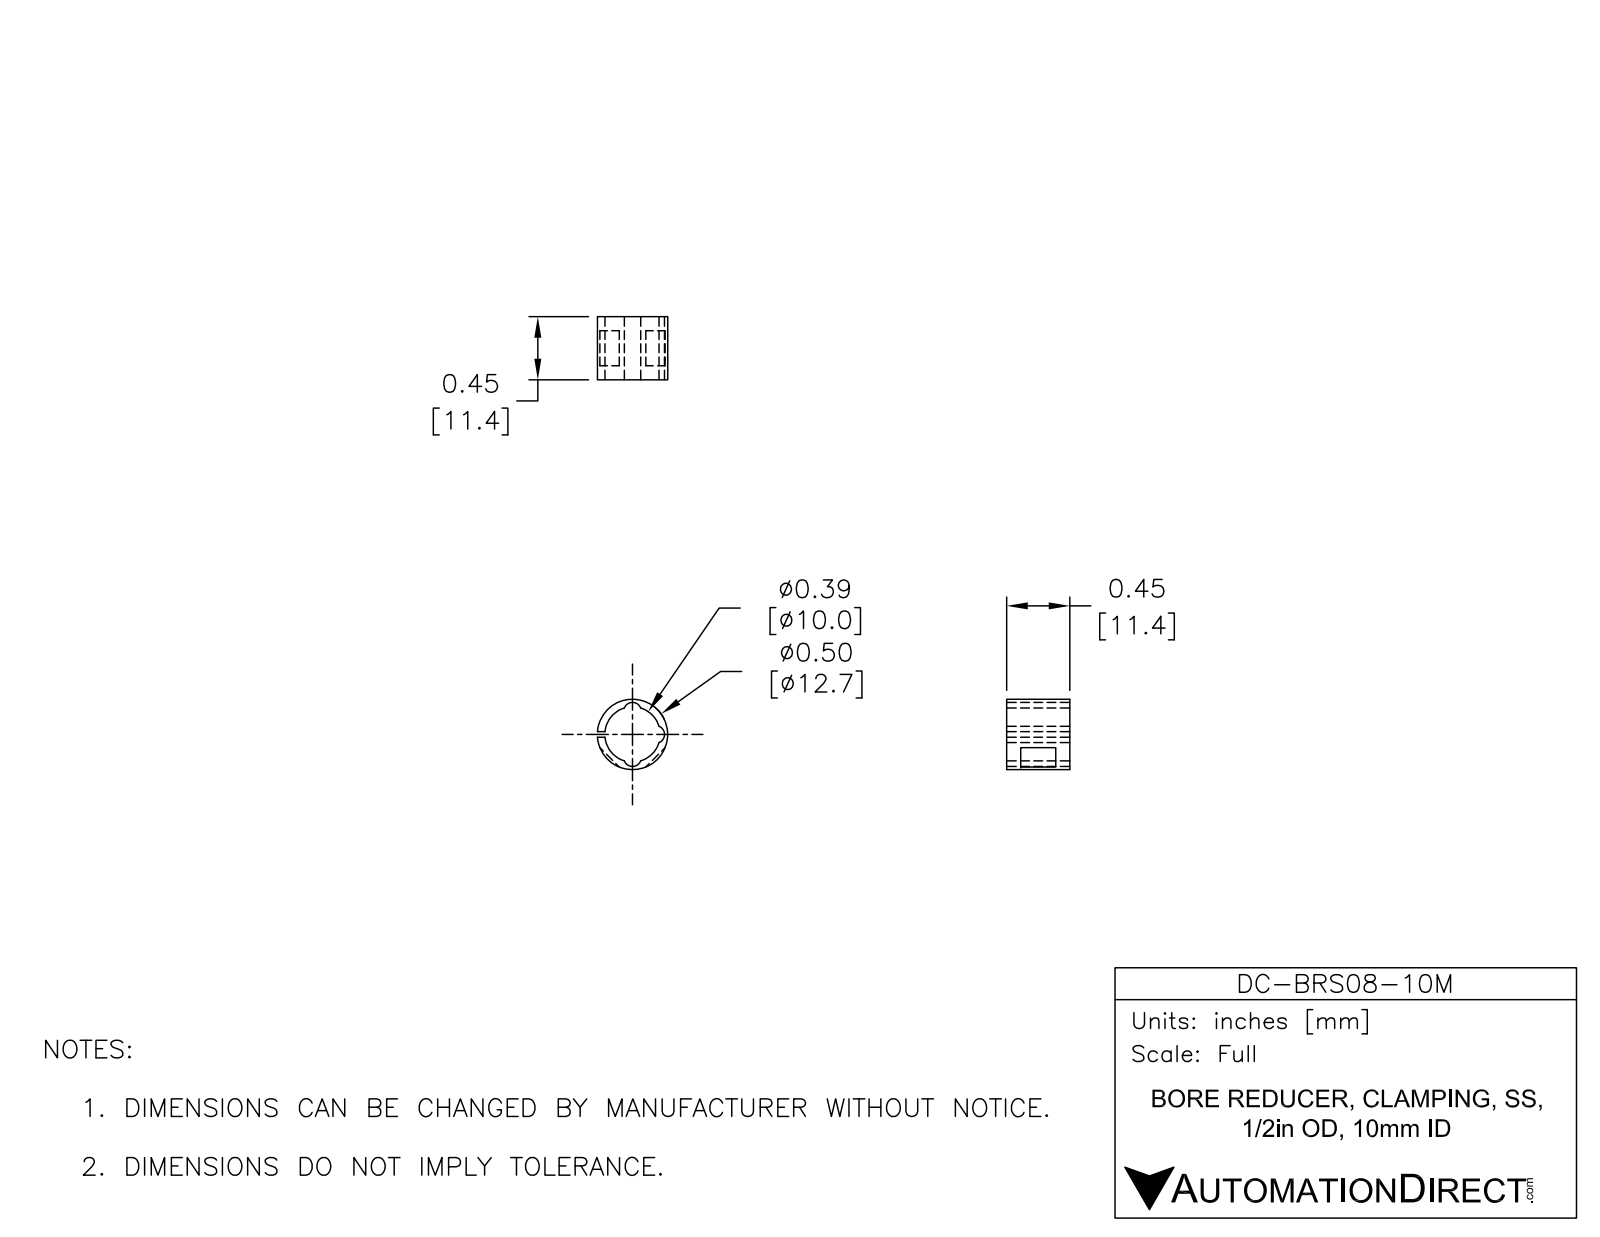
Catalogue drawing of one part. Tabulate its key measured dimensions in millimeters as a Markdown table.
| quantity | value |
| --- | --- |
| part name | DC-BRS08-10M |
| STEP written by | SolidWorks 2015 (AUTOMOTIVE_DESIGN) |
| units | millimeters |
| bodies | 1 solid, 21 faces (10 planar, 11 cylindrical, 0 other) |
| overall size | 12.7 × 12.68 × 11.4 |
| volume | 454 mm³ |
| surface area | 936 mm² |
| round bosses / shafts (diameter × count) | 12.7 × 1 |
| partial cylindrical surfaces (radius × count) | 1.59 × 3, 5 × 1 |
| main face-to-face distances | 11.4, 1.02, 2.54, 8.86, 6.32 |
